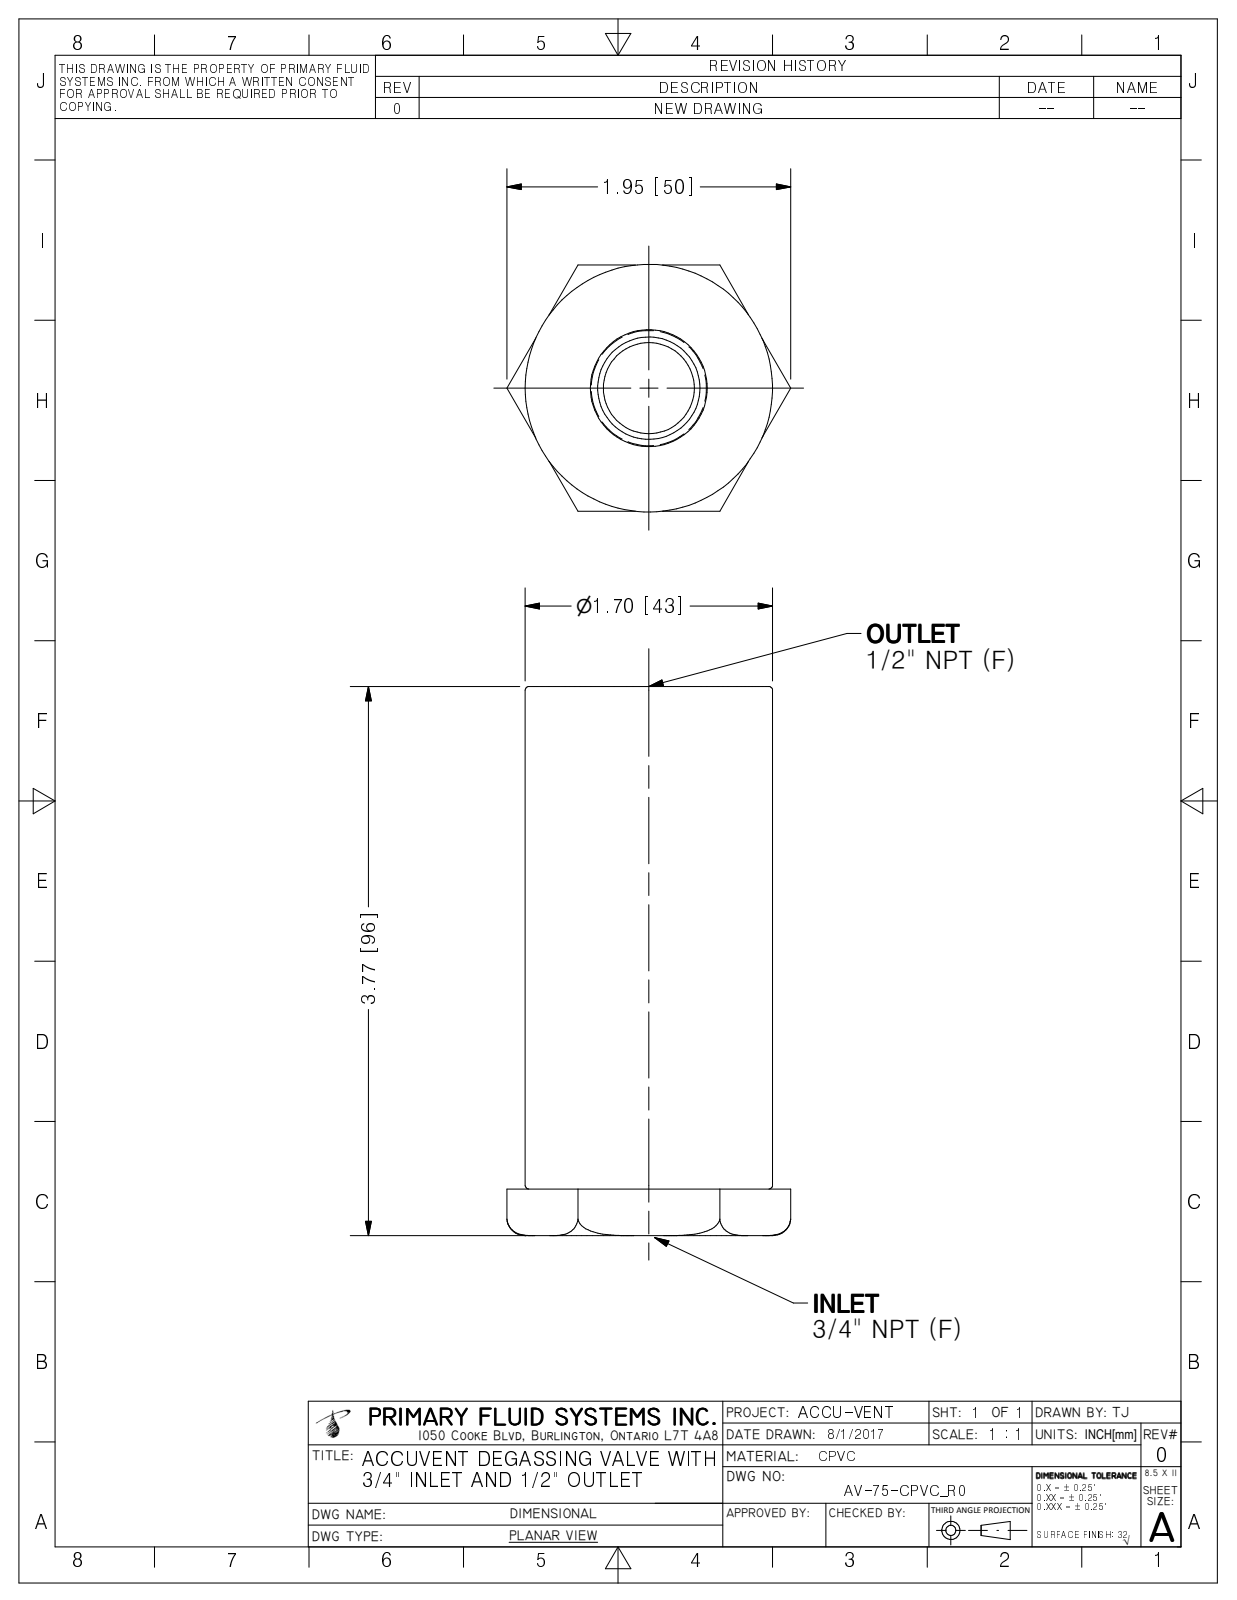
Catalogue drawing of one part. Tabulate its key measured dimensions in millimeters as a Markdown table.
| quantity | value |
| --- | --- |
| part name | AV-75-CPVC_R0 |
| STEP written by | Autodesk Inventor 2009 (AUTOMOTIVE_DESIGN) |
| units | millimeters |
| bodies | 1 solid, 23 faces (11 planar, 3 cylindrical, 9 other) |
| overall size | 95.8 × 49.6 × 43.2 |
| volume | 127 100 mm³ |
| surface area | 18 750 mm² |
| round holes (diameter × count) | 17.9 × 1, 26.7 × 1 |
| round bosses / shafts (diameter × count) | 43.2 × 1 |
| main face-to-face distances | 95.8, 42.9, 17, 78.7, 77.6, 60.6, 18.2, 8.1, 8.9, 69.5 |
